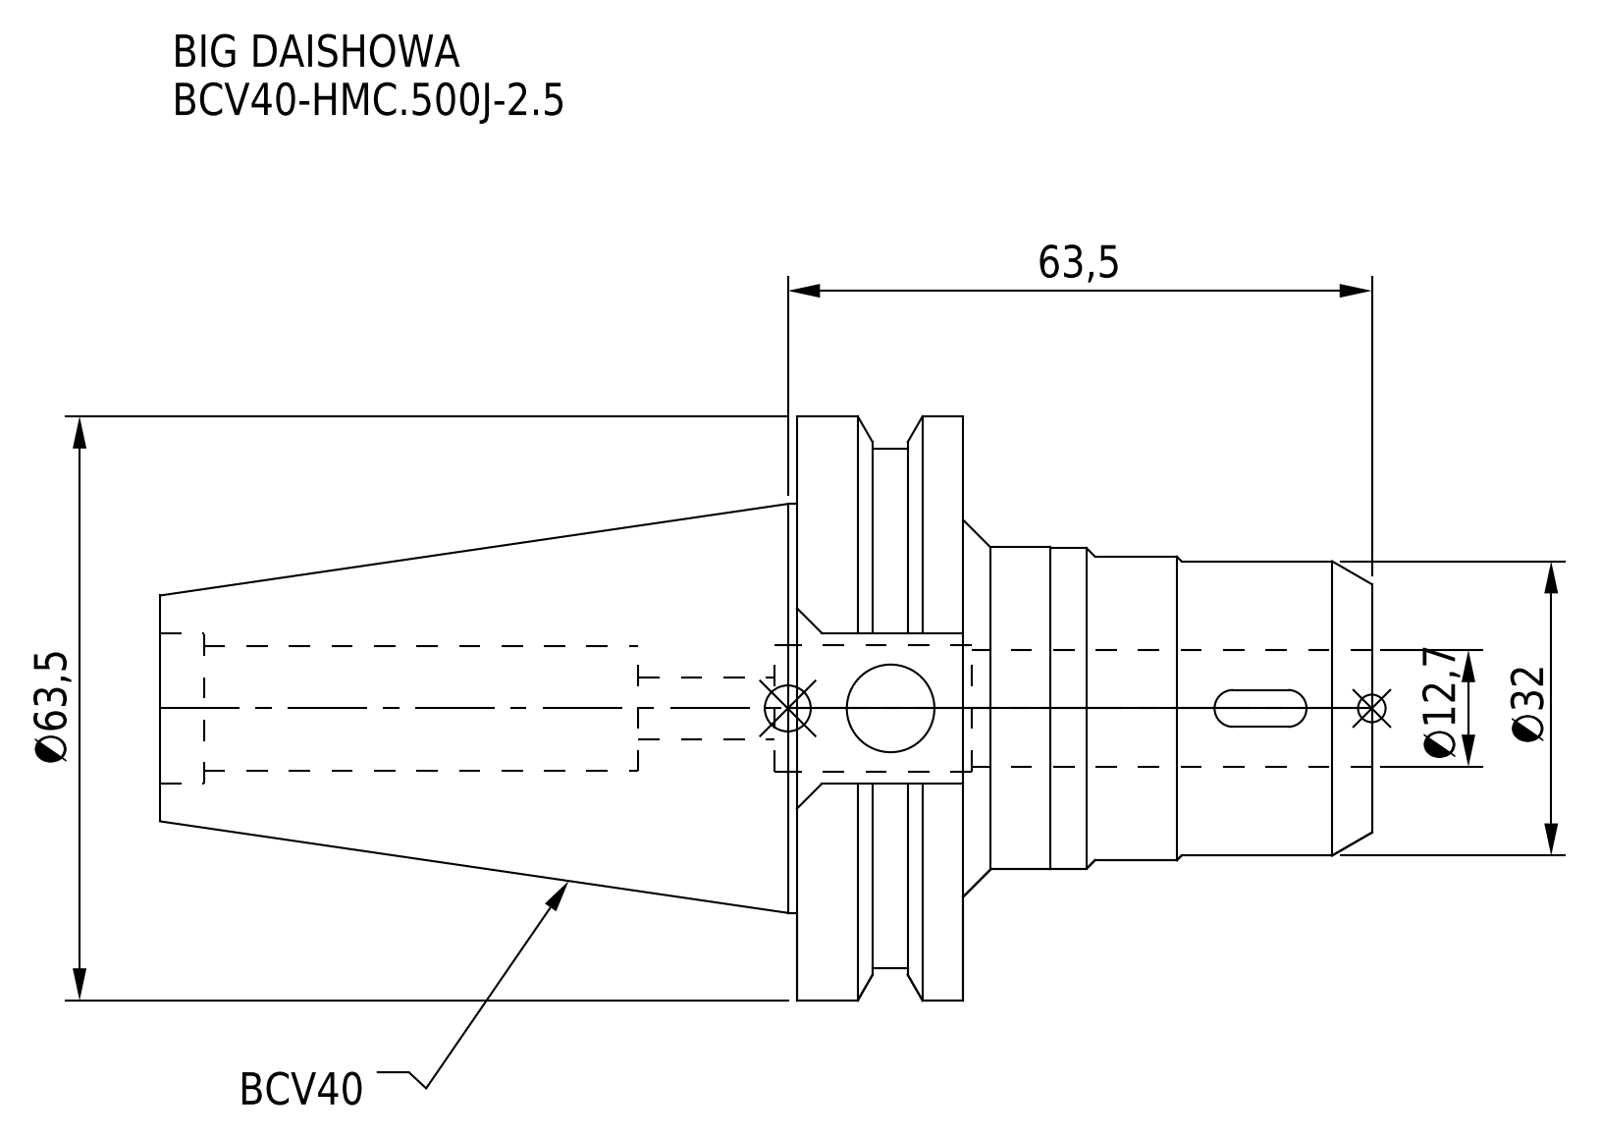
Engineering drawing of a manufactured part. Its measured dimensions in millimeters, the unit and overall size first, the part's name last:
Units: millimetres
Overall size (bounding box): 131.75 × 63.5 × 61.35
Round holes (diameter × count): ⌀6.8 ×1, ⌀9.53 ×1, ⌀12.7 ×1, ⌀13.6 ×1, ⌀13.7 ×1, ⌀16.32 ×1
Round bosses / shafts (diameter × count): ⌀63.5 ×1, ⌀56.36 ×1, ⌀44.45 ×1, ⌀35 ×1, ⌀34.8 ×1, ⌀33 ×1, ⌀32 ×1
Partial cylindrical surfaces — rounded edges, fillets, slot ends (radius × count): R2 ×4
Main face-to-face distances: 18.05, 44.45, 62.5, 131.75, 87.3, 69.25, 47.55, 16.38, 54.29, 9.84
Volume: 137 758 mm³ · Surface area: 26 574 mm²
Bodies: 1 solid, 88 faces (36 planar, 38 cylindrical, 14 other)
Part name (STEP PRODUCT): BCV40-HMC_500J-2_5
STEP written by: CREO PARAMETRIC BY PTC INC, 2016380 (AUTOMOTIVE_DESIGN)
